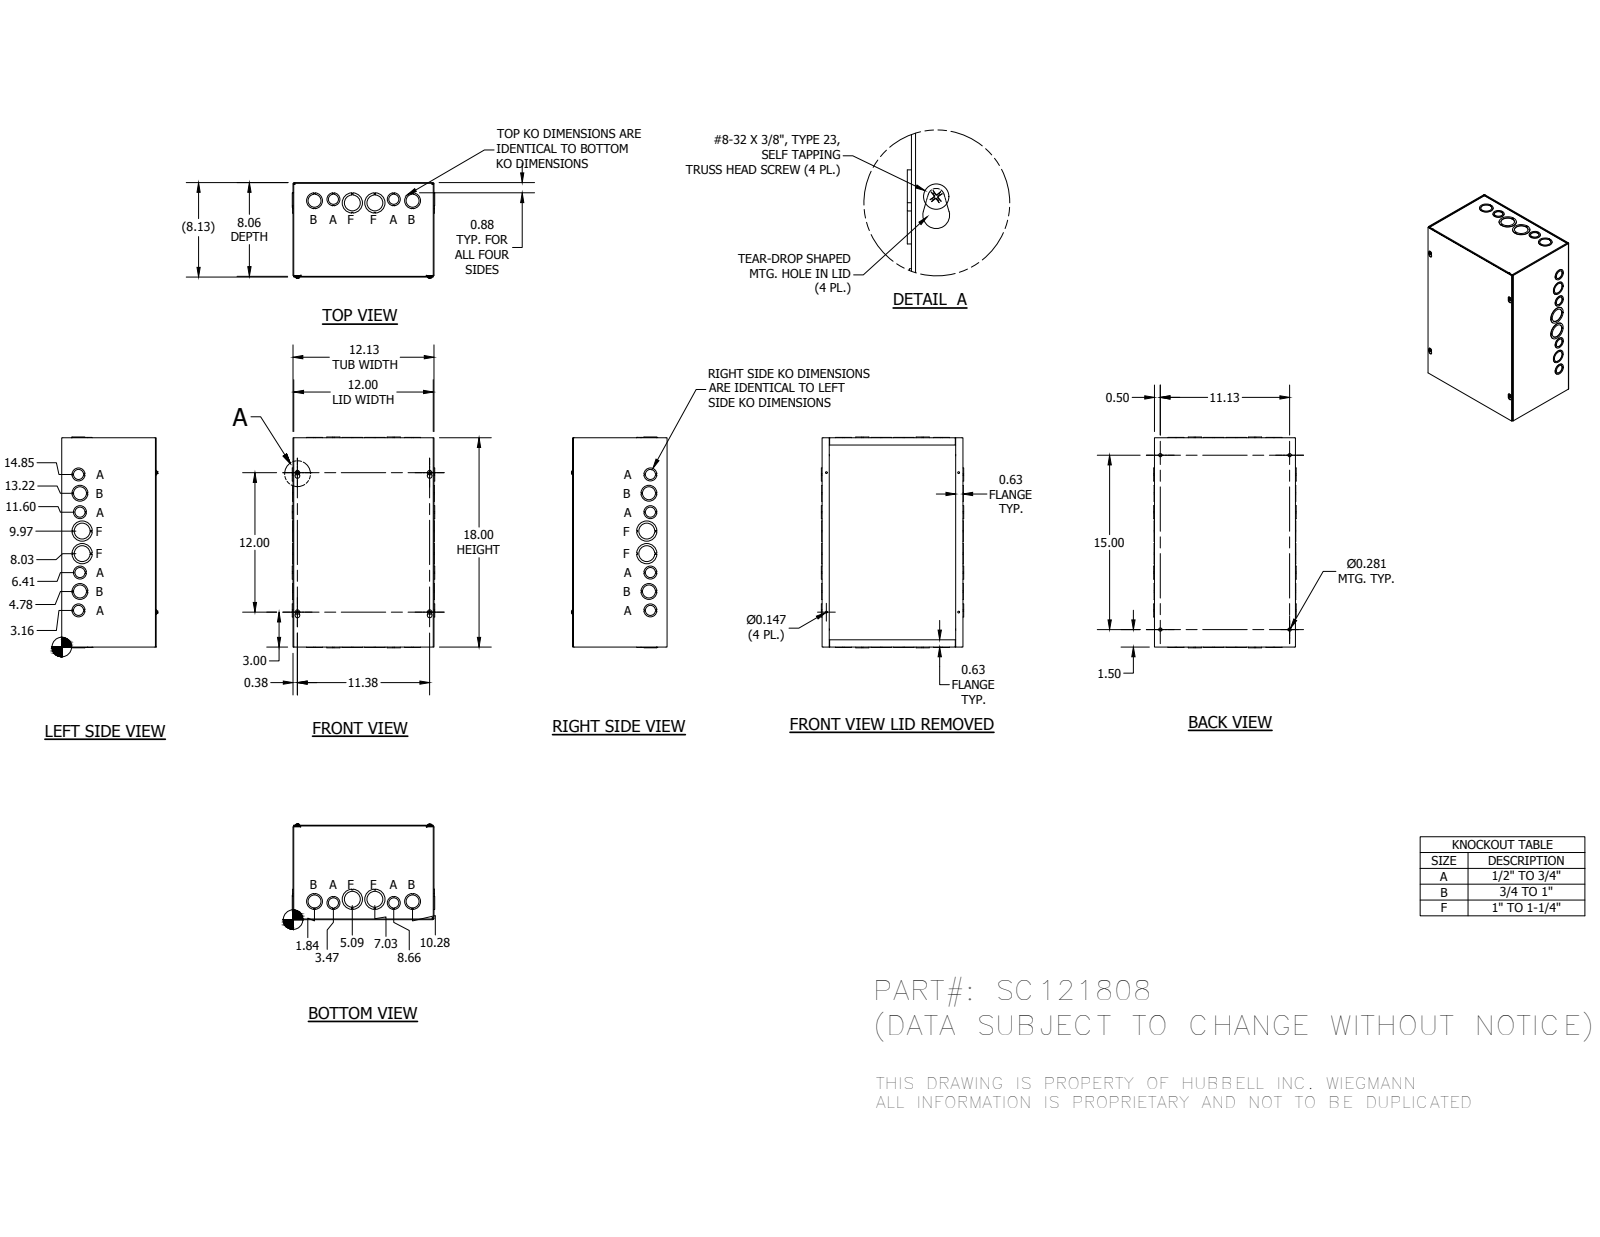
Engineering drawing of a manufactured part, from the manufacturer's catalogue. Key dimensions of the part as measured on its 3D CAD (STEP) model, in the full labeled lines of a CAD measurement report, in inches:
Part name (STEP PRODUCT): SC121808BLR; SC1208TB; SC1218LPA; 34056 (+1 more)
STEP written by: Autodesk Inventor 2014 (AUTOMOTIVE_DESIGN)
Units: inches
Bodies: 29 solids, 1055 faces (771 planar, 216 cylindrical, 68 other)
Overall size (bounding box): 18.125 × 12.25 × 8.225
Round holes (diameter × count): ⌀1.125 ×12, ⌀0.875 ×8, ⌀1.375 ×8, ⌀0.147 ×4, ⌀0.281 ×4, ⌀1.75 ×4
Round bosses / shafts (diameter × count): ⌀0.384 ×4, ⌀0.164 ×4
Partial cylindrical surfaces — rounded edges, fillets, slot ends (radius × count): R0.031 ×12, R0.094 ×12, R0.125 ×4, R0.203 ×4
Main face-to-face distances: 0.063, 12.063, 8, 0.062, 8.062, 8.063, 8.125, 17.937, 12, 12.125
Hole centre spacings: 1.505, 1.63, 1.655, 3.256, 3.579, 5.194, 6.816, 11.35
